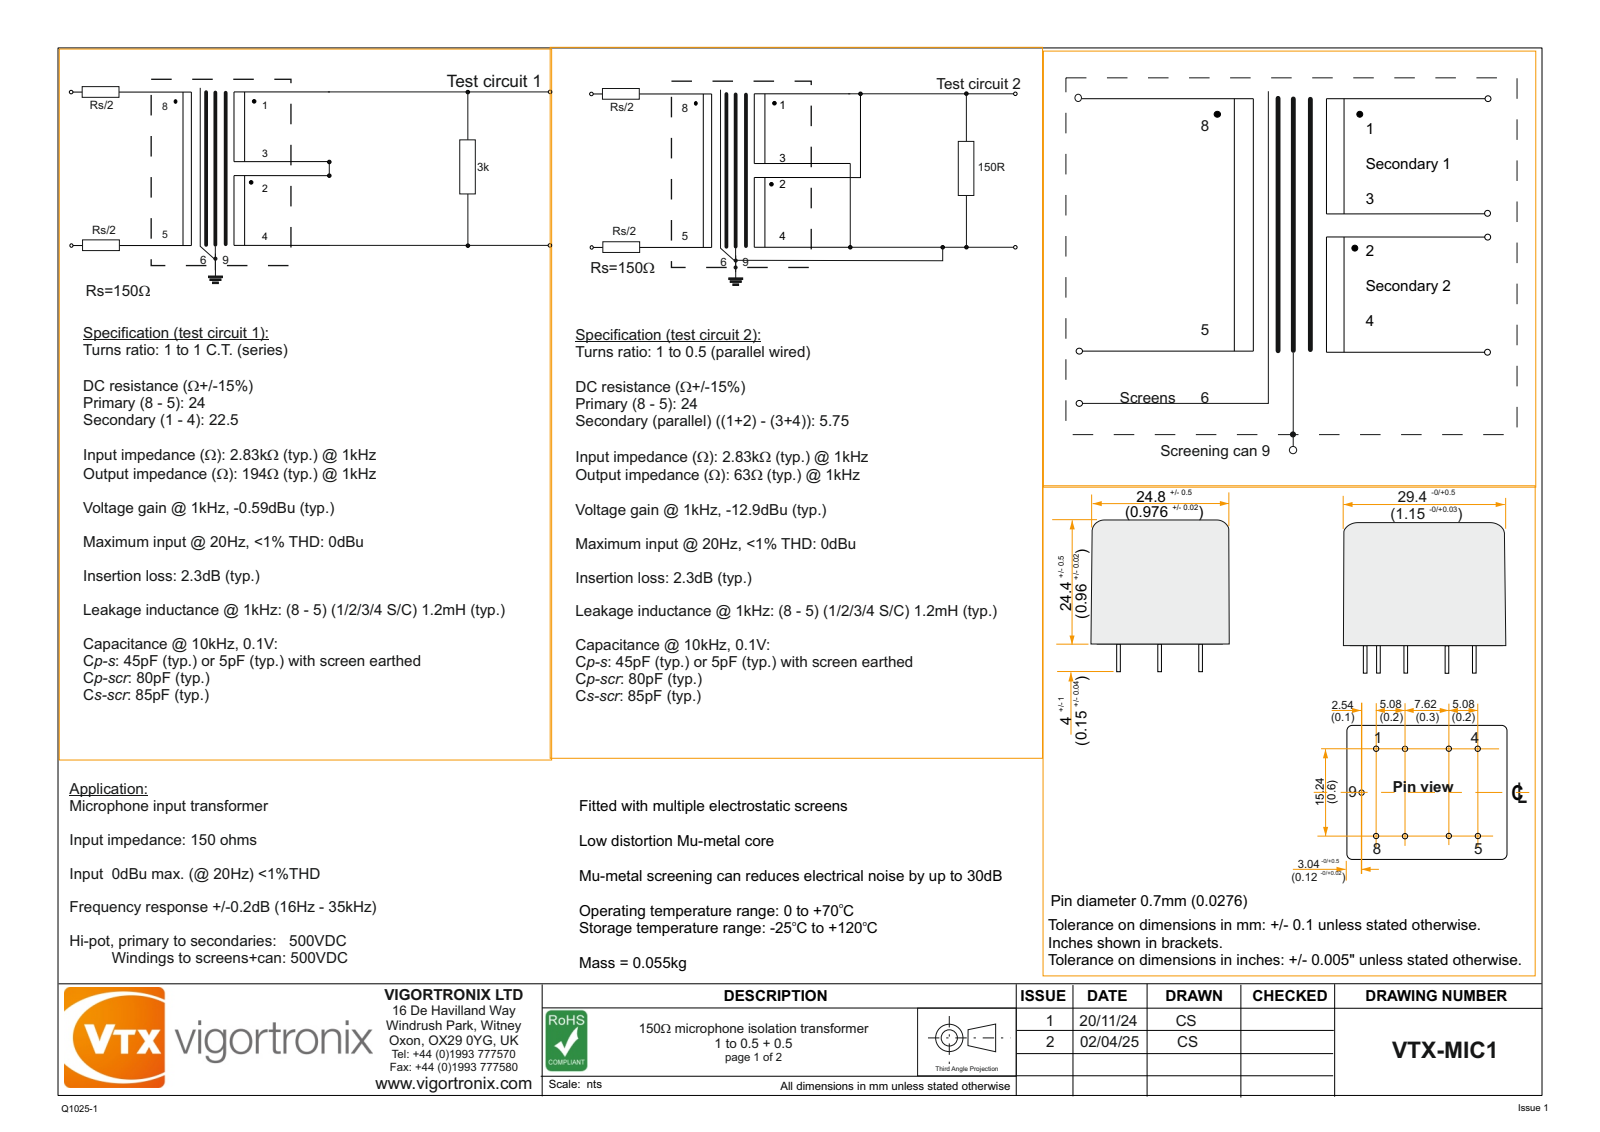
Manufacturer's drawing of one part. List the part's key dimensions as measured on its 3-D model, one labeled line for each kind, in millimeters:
Part name (STEP PRODUCT): VTX-MIC1; VTX-MIC1 CAN; VTX-MIC1 BOBBIN; VTX-MIC1 LID
STEP written by: SolidWorks 2024 (AUTOMOTIVE_DESIGN)
Units: millimetres
Bodies: 3 solids, 130 faces (36 planar, 74 cylindrical, 20 other)
Overall size (bounding box): 29.62 × 28.6 × 25.22
Volume: 15 314 mm³ · Surface area: 10 856 mm²
Round holes (diameter × count): ⌀3.5 ×8, ⌀1.5 ×1
Round bosses / shafts (diameter × count): ⌀0.7 ×8
Partial cylindrical surfaces — rounded edges, fillets, slot ends (radius × count): R0.5 ×20, R1.9 ×8, R2.5 ×8, R2 ×4
Main face-to-face distances: 0.6, 23.4, 22.8, 22.5, 0.9, 23.1, 24, 23, 27.5, 2.6
Hole centre spacings: 5.08, 12.7, 15.24, 16.06, 17.04, 19.84, 7.62, 8.03
